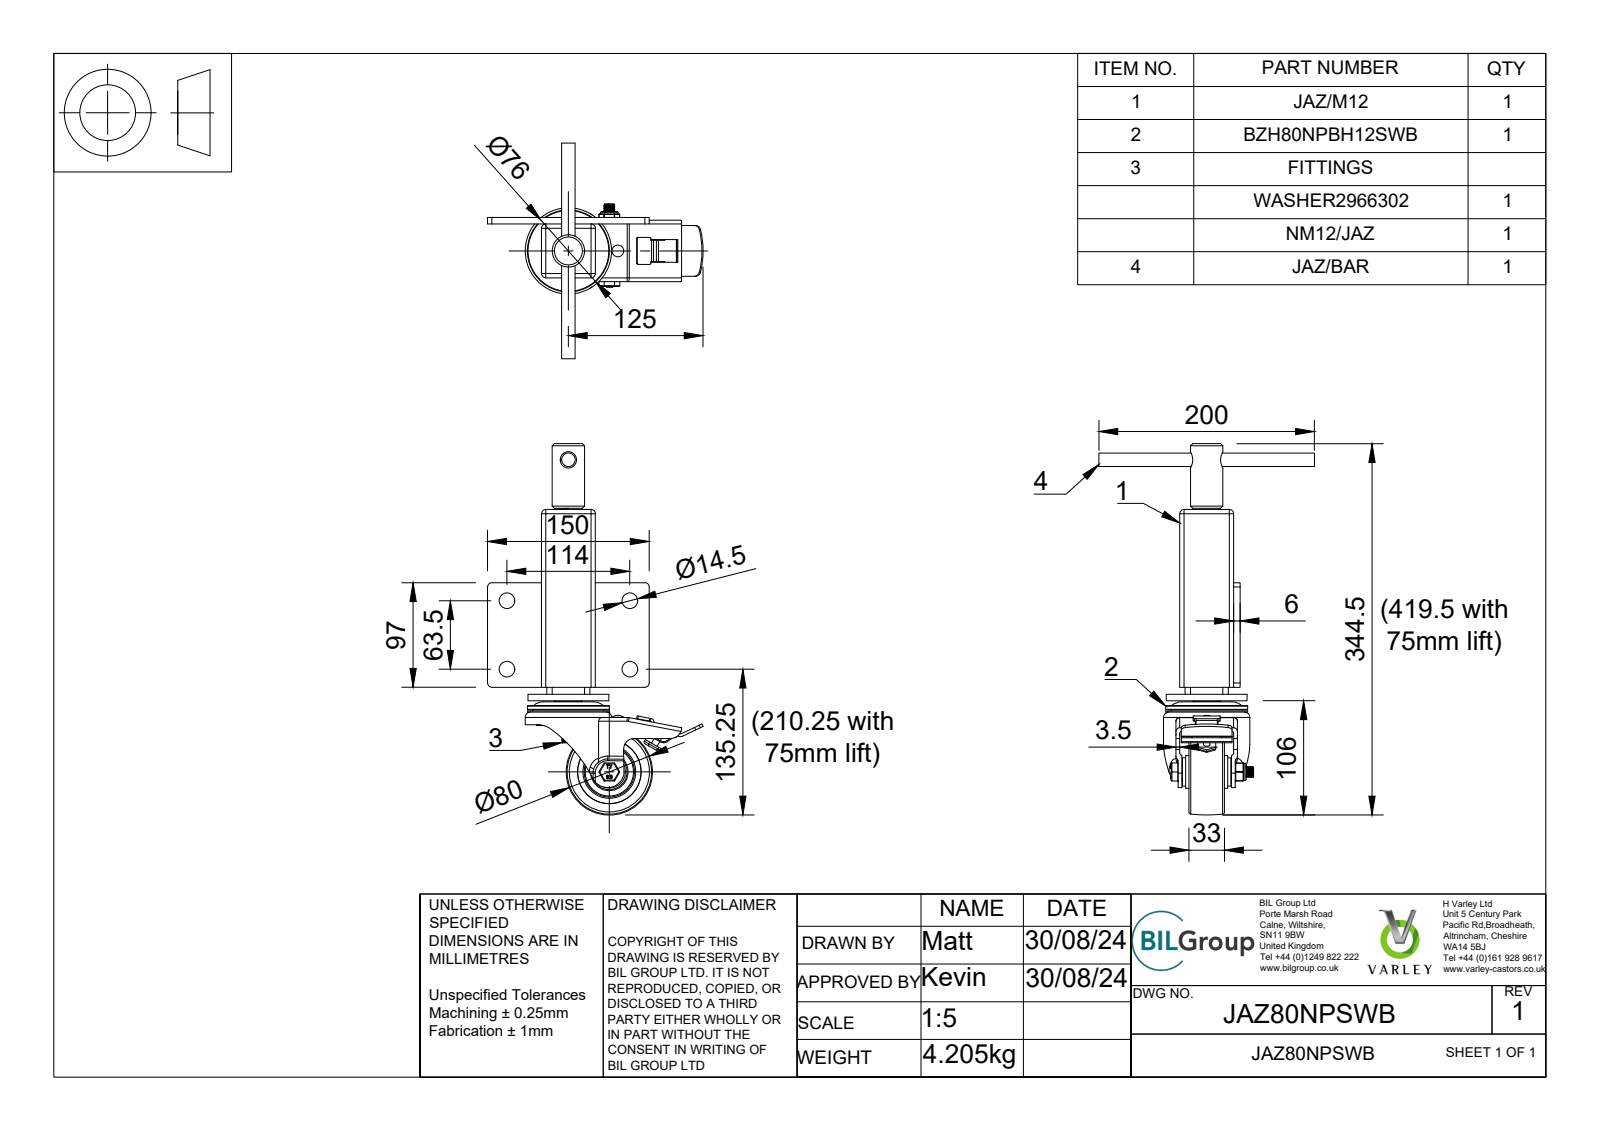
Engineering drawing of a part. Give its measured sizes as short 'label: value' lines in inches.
name: JAZ80NPSWB v2; BZH80ASBH12SWB v1; ZINC PLATED, PRESSED STEEL TOP PLATE; ZINC PLATED, PRESSED STEEL FORKS (+7 more)
written by: Autodesk Translation Framework v13.14.0.145 (AUTOMOTIVE_DESIGN)
unit: in
bodies: 48 solids, 1105 faces (484 planar, 441 cylindrical, 180 other)
size: 13.563 × 7.874 × 7.874
volume: 37.91 in³; area: 487.1 in²
holes: 4× ⌀0.571, 2× ⌀0.236, 2× ⌀0.472, 2× ⌀0.512, 1× ⌀0.394, 1× ⌀0.402, 1× ⌀0.48, 1× ⌀0.492, 1× ⌀0.594, 1× ⌀0.819, 1× ⌀0.886, 1× ⌀0.945
bosses: 8× ⌀0.148, 1× ⌀2.992, 1× ⌀2.953, 1× ⌀2.598, 1× ⌀2.323, 1× ⌀1.929, 1× ⌀1.378, 1× ⌀1.181
rounds: 24× R0.02, 16× R0.157, 14× R0.039, 14× R0.098, 11× R0.079, 10× R0.069, 9× R0.197, 8× R0.138
face distances: 0.098, 1.87, 1.772, 0.236, 0.197, 1.673, 0.335, 1.575, 1.969, 0.295
hole spacings: 2.5, 4.488, 5.137, 5.614, 7.968, 1.807, 3.824, 5.296
